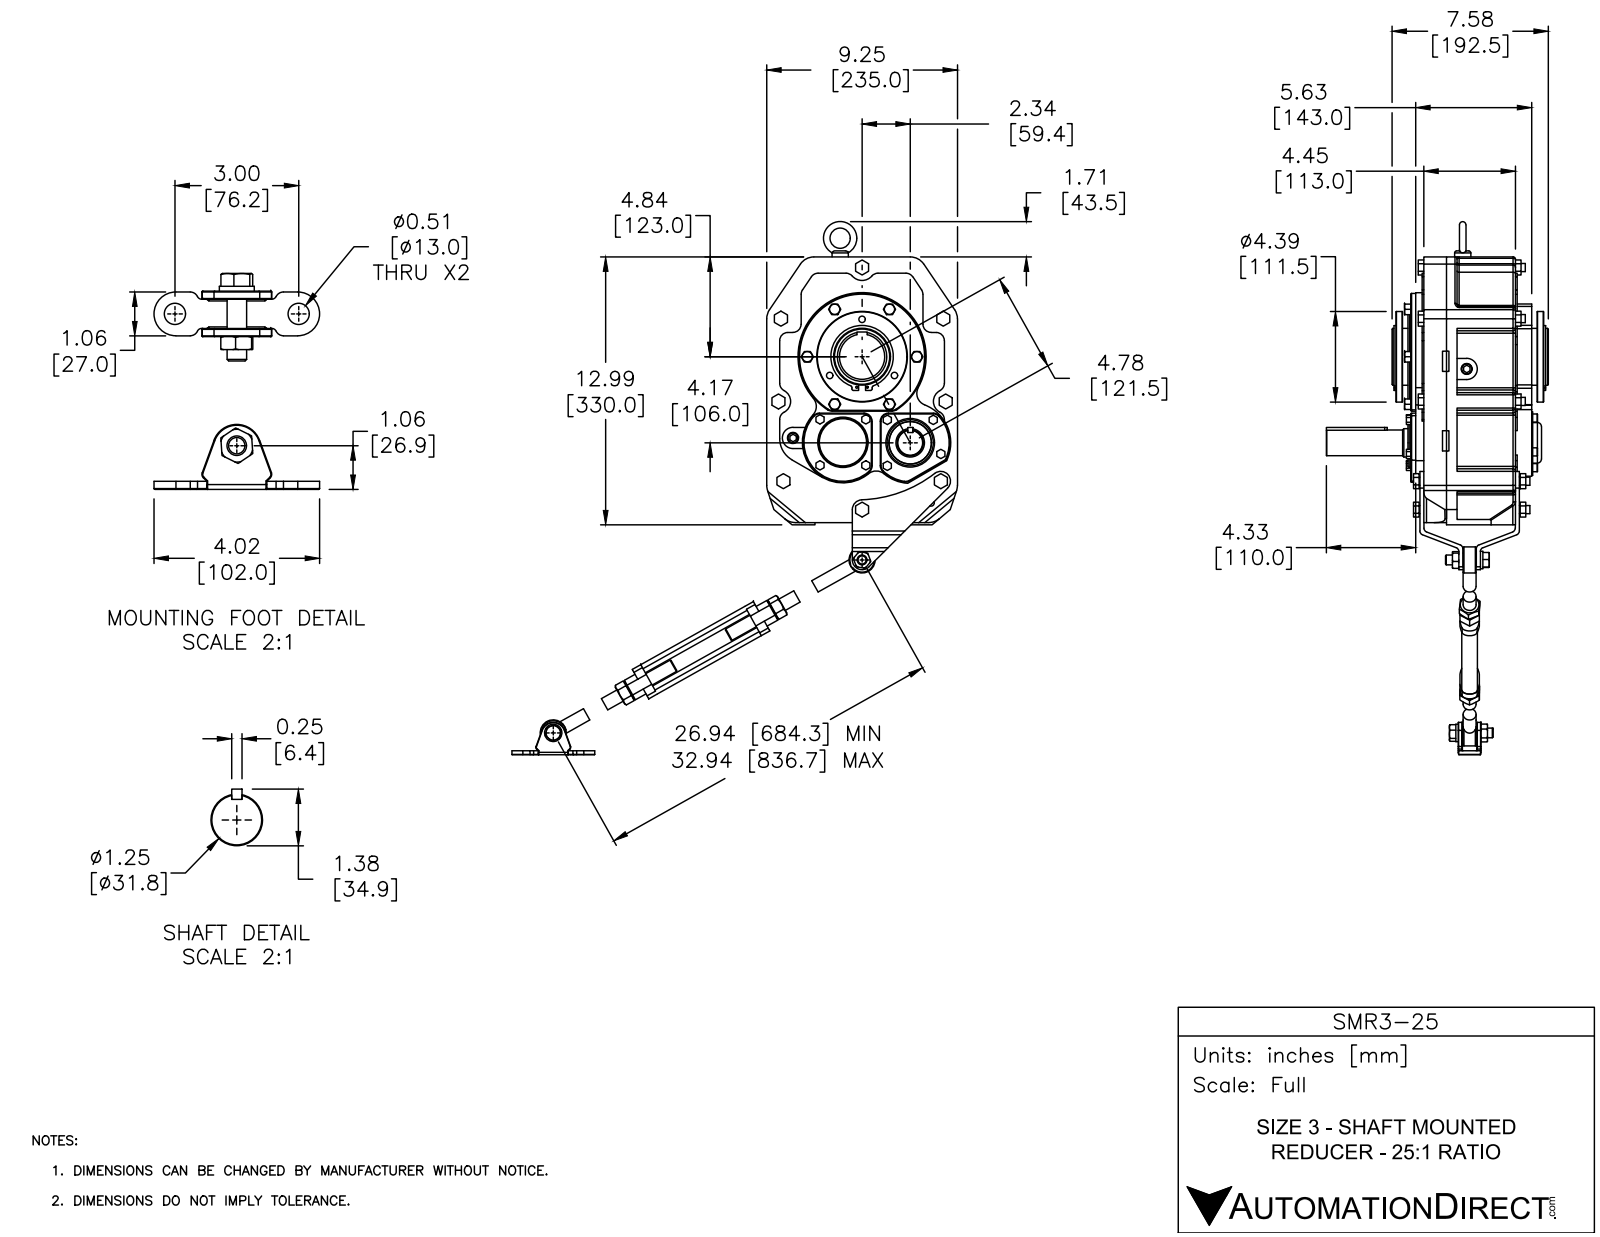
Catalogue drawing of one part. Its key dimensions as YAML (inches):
part_name: "SMR3-TA_1; SMR3-25; SMR3-TA; SMR3-TA_5 (+4 more)"
step_written_by: "SolidWorks 2016 (AUTOMOTIVE_DESIGN)"
units: inches
bodies: {solids: 71, faces: 1559, planar: 727, cylindrical: 556, other: 276}
overall_size: [33.892, 32.734, 10.768]
volume: 540.7
surface_area: 1421
round_holes:
  - {diameter: 0.394, count: 8}
  - {diameter: 0.433, count: 8}
  - {diameter: 0.313, count: 7}
  - {diameter: 0.512, count: 5}
  - {diameter: 0.5, count: 4}
  - {diameter: 0.098, count: 2}
  - {diameter: 0.472, count: 2}
  - {diameter: 0.48, count: 2}
  - {diameter: 0.508, count: 2}
  - {diameter: 0.524, count: 2}
  - {diameter: 0.63, count: 2}
  - {diameter: 0.315, count: 1}
round_bosses_or_shafts:
  - {diameter: 0.512, count: 5}
  - {diameter: 0.394, count: 4}
  - {diameter: 2.362, count: 2}
  - {diameter: 1.969, count: 2}
  - {diameter: 1.26, count: 2}
  - {diameter: 0.878, count: 2}
  - {diameter: 0.846, count: 2}
  - {diameter: 0.63, count: 2}
partial_cylinders:
  - {radius: 0.118, count: 80}
  - {radius: 0.394, count: 35}
  - {radius: 0.02, count: 22}
  - {radius: 0.197, count: 16}
  - {radius: 0.098, count: 12}
  - {radius: 0.787, count: 10}
  - {radius: 0.591, count: 9}
  - {radius: 0.039, count: 7}
face_to_face_distances: [0.394, 1.496, 4.528, 0.079, 1.102, 5.63, 5.236, 4.134, 0.315, 0.709]
hole_center_spacings: [2.756, 3.898, 1.813, 3.139, 1.109, 1.432, 1.498, 1.757]
